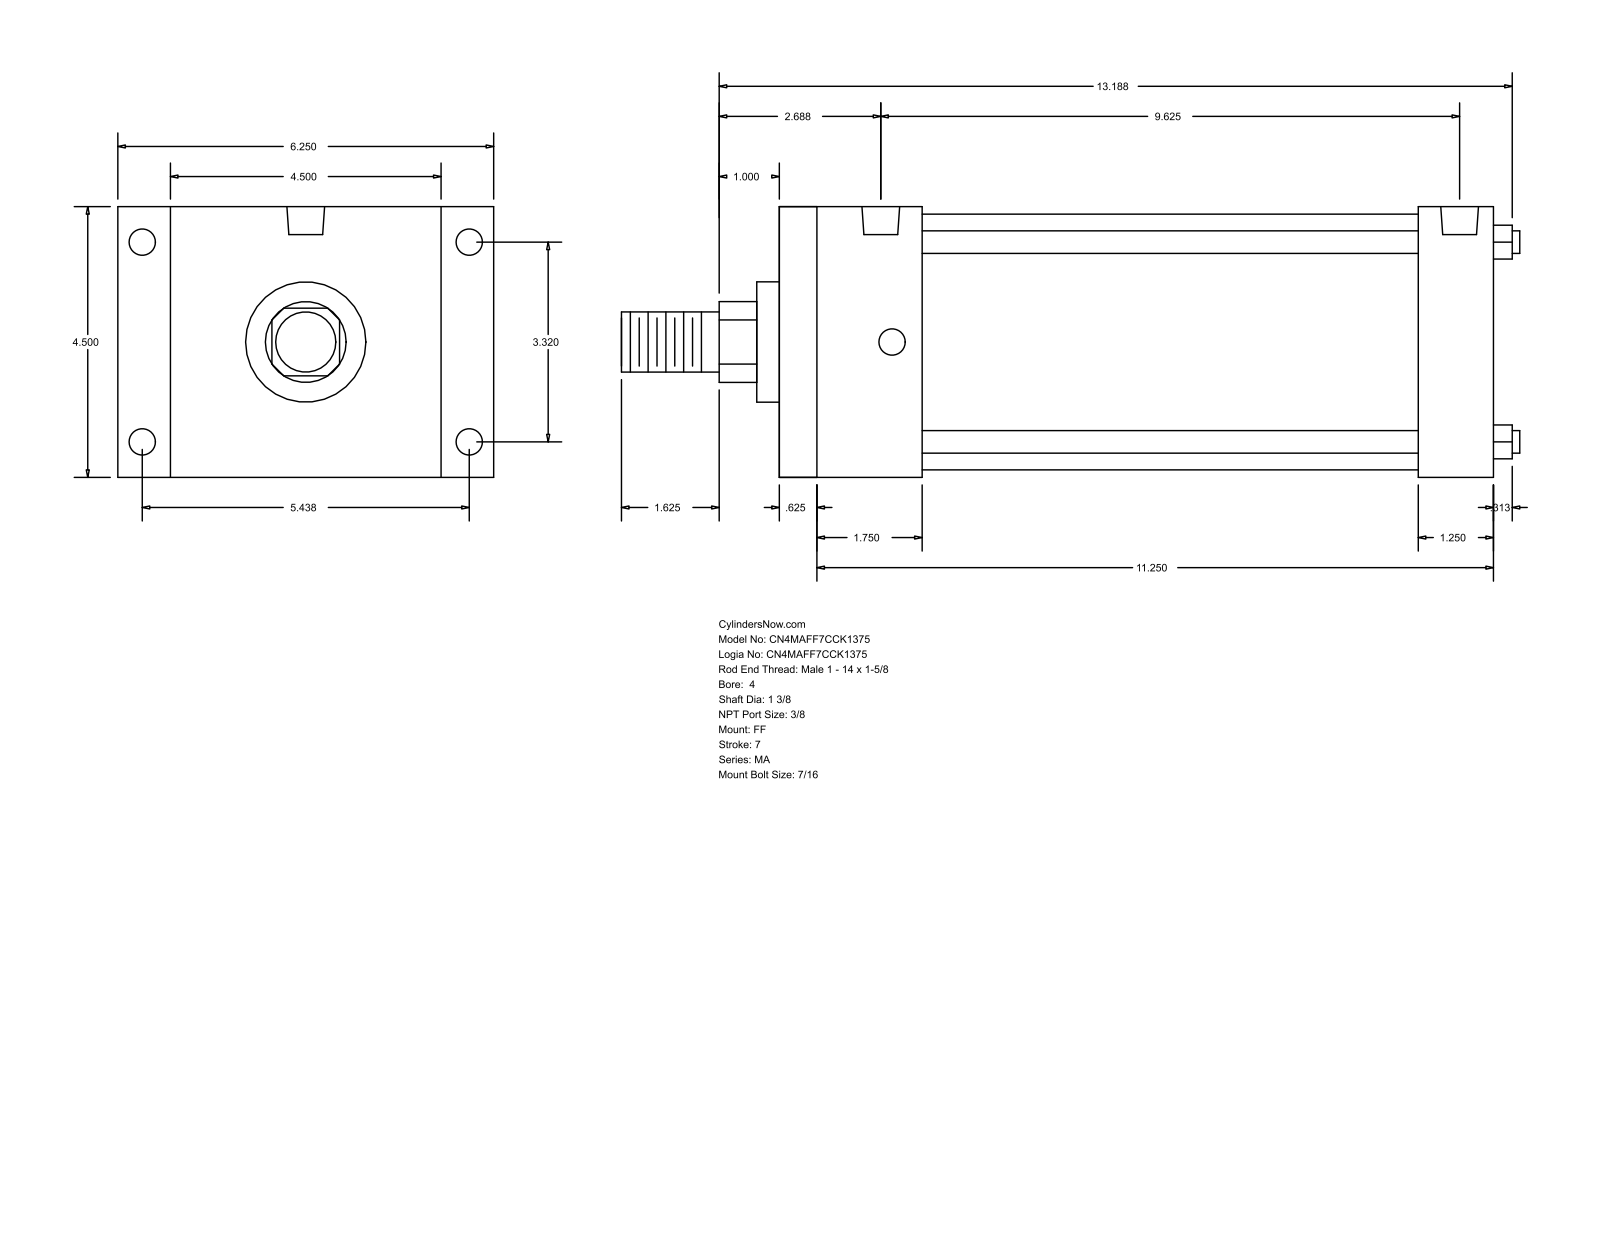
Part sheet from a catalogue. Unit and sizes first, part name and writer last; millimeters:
Units: millimetres
Overall size (bounding box): 379.41 × 158.75 × 114.3
Round holes (diameter × count): ⌀11.11 ×8, ⌀15.93 ×2
Round bosses / shafts (diameter × count): ⌀9.53 ×4, ⌀107.95 ×1, ⌀50.8 ×1, ⌀34.92 ×1, ⌀25.4 ×1
Partial cylindrical surfaces — rounded edges, fillets, slot ends (radius × count): R17.06 ×1
Main face-to-face distances: 114.3, 301.62, 15.87, 285.75, 22.23, 136.53, 269.87, 254, 31.75, 60.32
Hole centre spacings: 84.32, 138.12, 161.82, 234.95, 4.76, 4.77, 239.71, 239.72
Bodies: 0 solids, 92 faces (64 planar, 28 cylindrical, 0 other)
Part name (STEP PRODUCT): MA_FF__0400_1.375
STEP written by: GSSL Pune (CONFIG_CONTROL_DESIGN)
